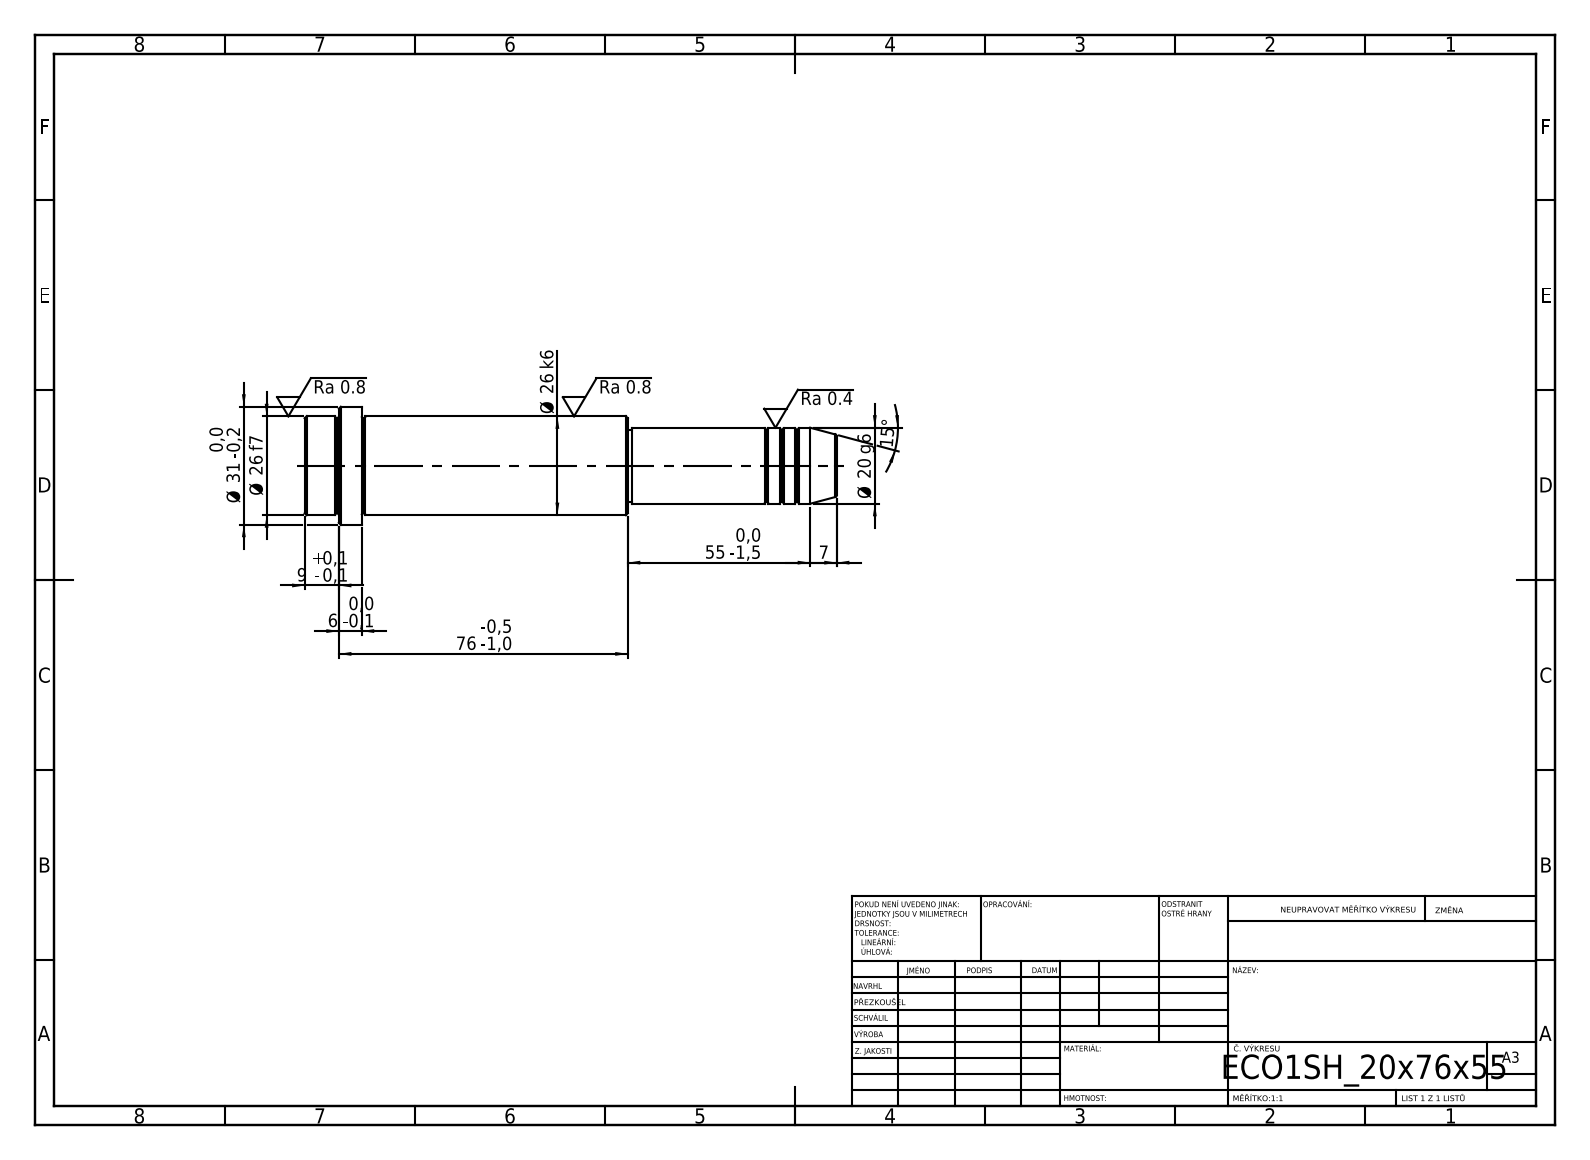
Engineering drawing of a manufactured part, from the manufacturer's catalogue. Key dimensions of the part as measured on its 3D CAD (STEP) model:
STEP written by: SolidWorks 2019 (CONFIG_CONTROL_DESIGN)
Units: millimetres
Bodies: 1 solid, 52 faces (6 planar, 16 cylindrical, 30 other)
Overall size (bounding box): 140 × 31 × 31
Volume: 63 164 mm³ · Surface area: 12 029 mm²
Round bosses / shafts (diameter × count): ⌀31 ×1, ⌀26 ×1, ⌀20 ×1, ⌀19 ×1
Main face-to-face distances: 15, 70, 85, 55, 125, 140, 131, 76, 6, 9
